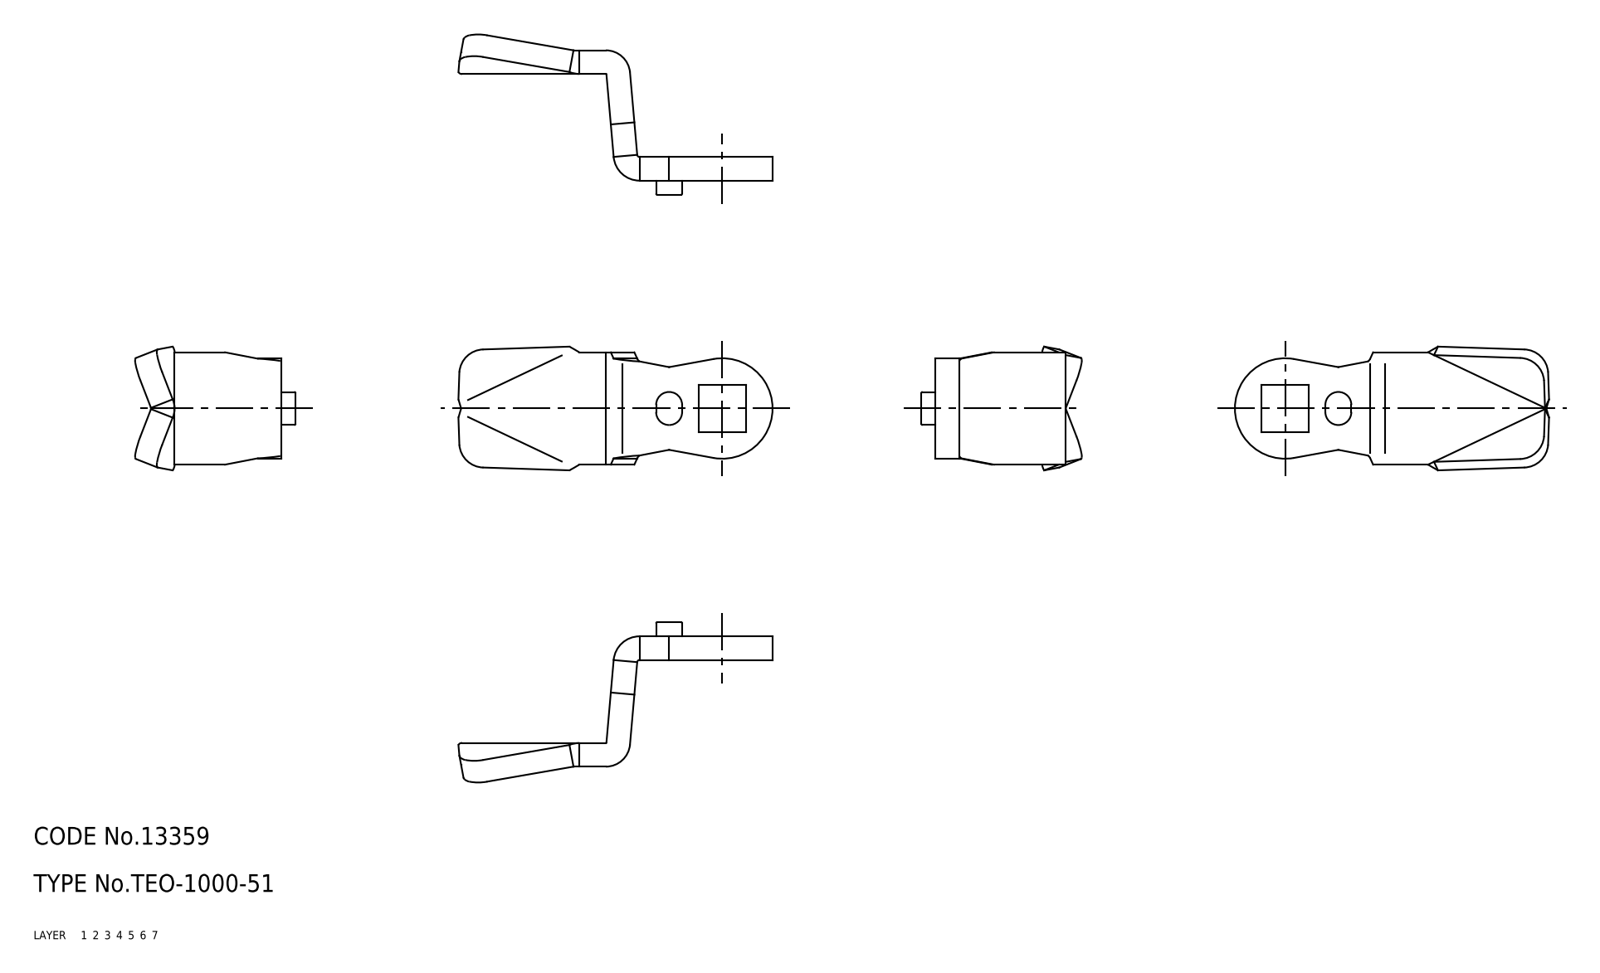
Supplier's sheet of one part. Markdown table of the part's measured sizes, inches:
| quantity | value |
| --- | --- |
| part name | cam |
| STEP written by | CADfix (AUTOMOTIVE_DESIGN) |
| units | inches |
| bodies | 1 solid, 55 faces (0 planar, 0 cylindrical, 55 other) |
| overall size | 2.124 × 1.097 × 0.824 |
| volume | 0.276 in³ |
| surface area | 4.873 in² |
